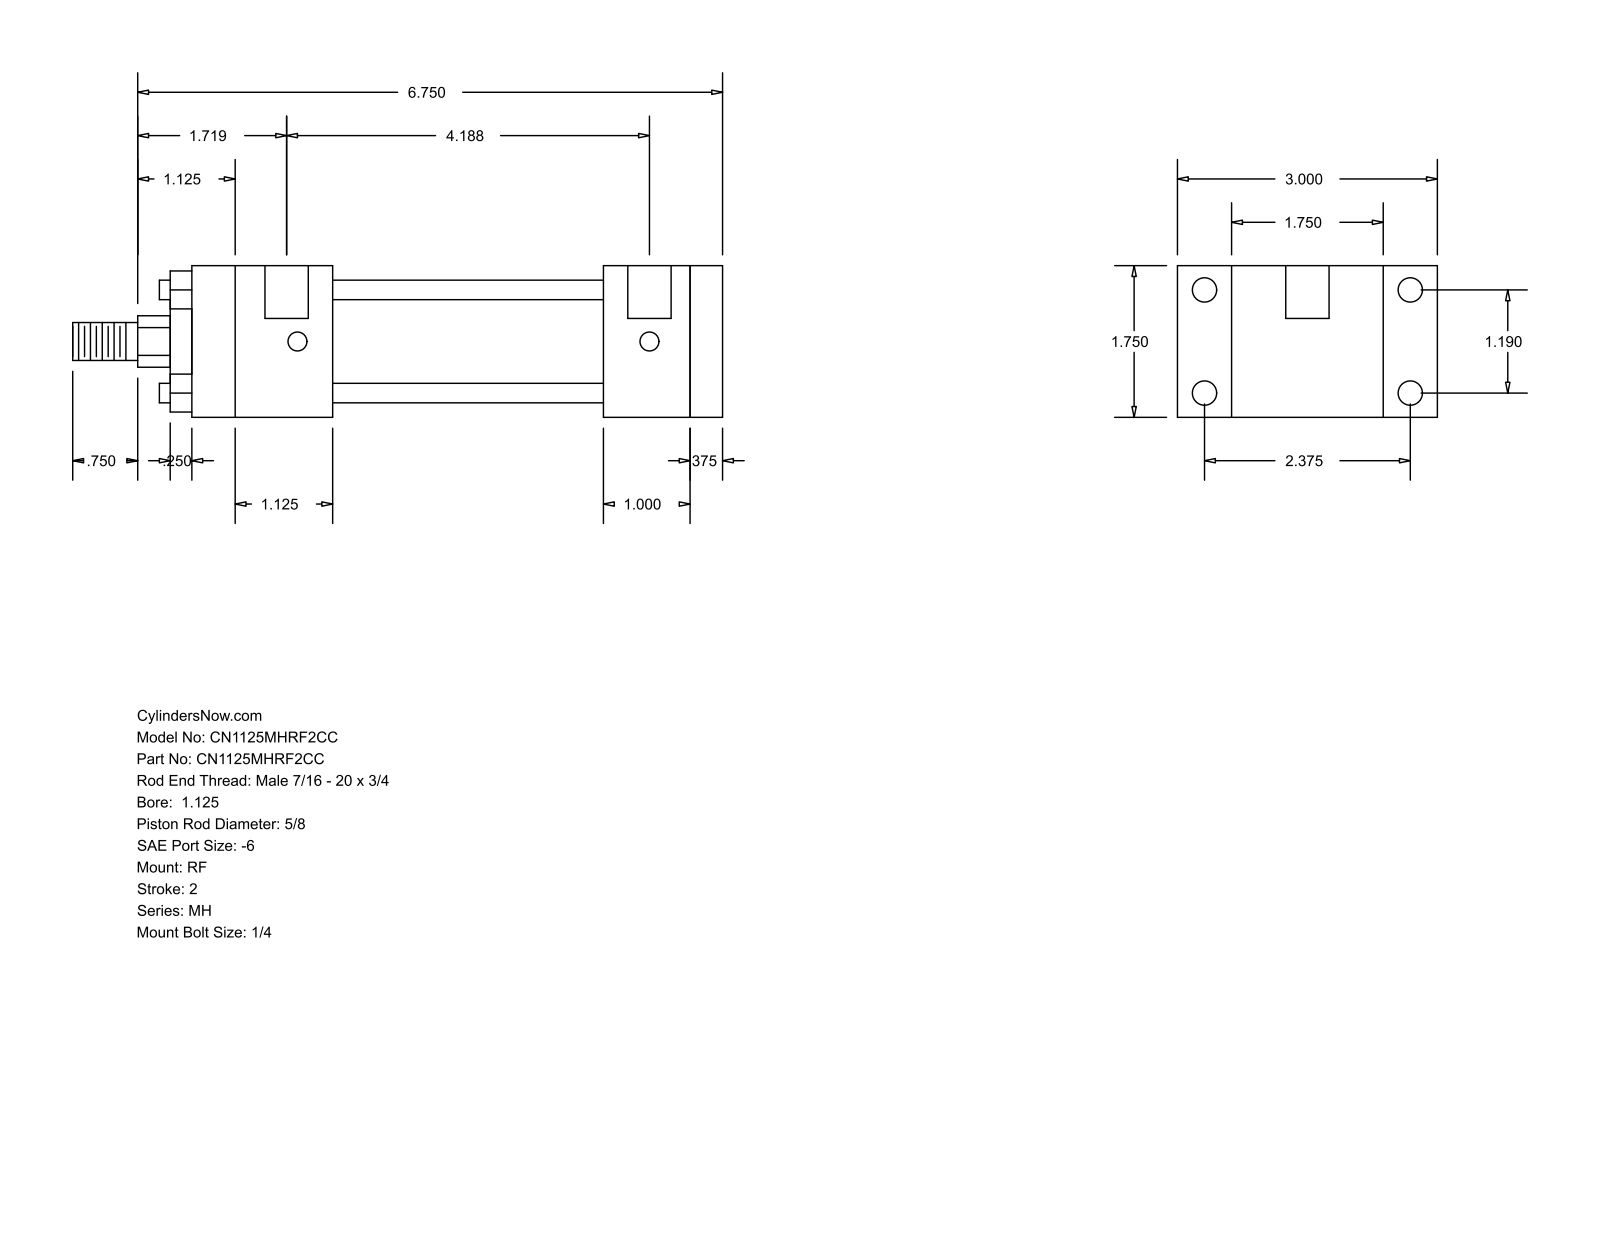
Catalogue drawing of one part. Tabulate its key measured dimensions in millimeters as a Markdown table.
| quantity | value |
| --- | --- |
| part name | MH_RF__0112_0.625 |
| STEP written by | GSSL Pune (CONFIG_CONTROL_DESIGN) |
| units | millimeters |
| bodies | 0 solids, 92 faces (64 planar, 28 cylindrical, 0 other) |
| overall size | 190.5 × 76.2 × 44.45 |
| round holes (diameter × count) | 5.56 × 4, 7.14 × 4, 12.7 × 2 |
| round bosses / shafts (diameter × count) | 5.71 × 4, 34.92 × 1, 28.57 × 1, 15.88 × 1, 11.11 × 1 |
| partial cylindrical surfaces (radius × count) | 7.54 × 1 |
| main face-to-face distances | 44.46, 9.52, 25.4, 15.87, 104.78, 114.3, 79.38, 34.92, 41.27, 120.65 |
| hole center spacings | 30.22, 60.32, 67.47, 103.19, 3.17, 106.36 |
